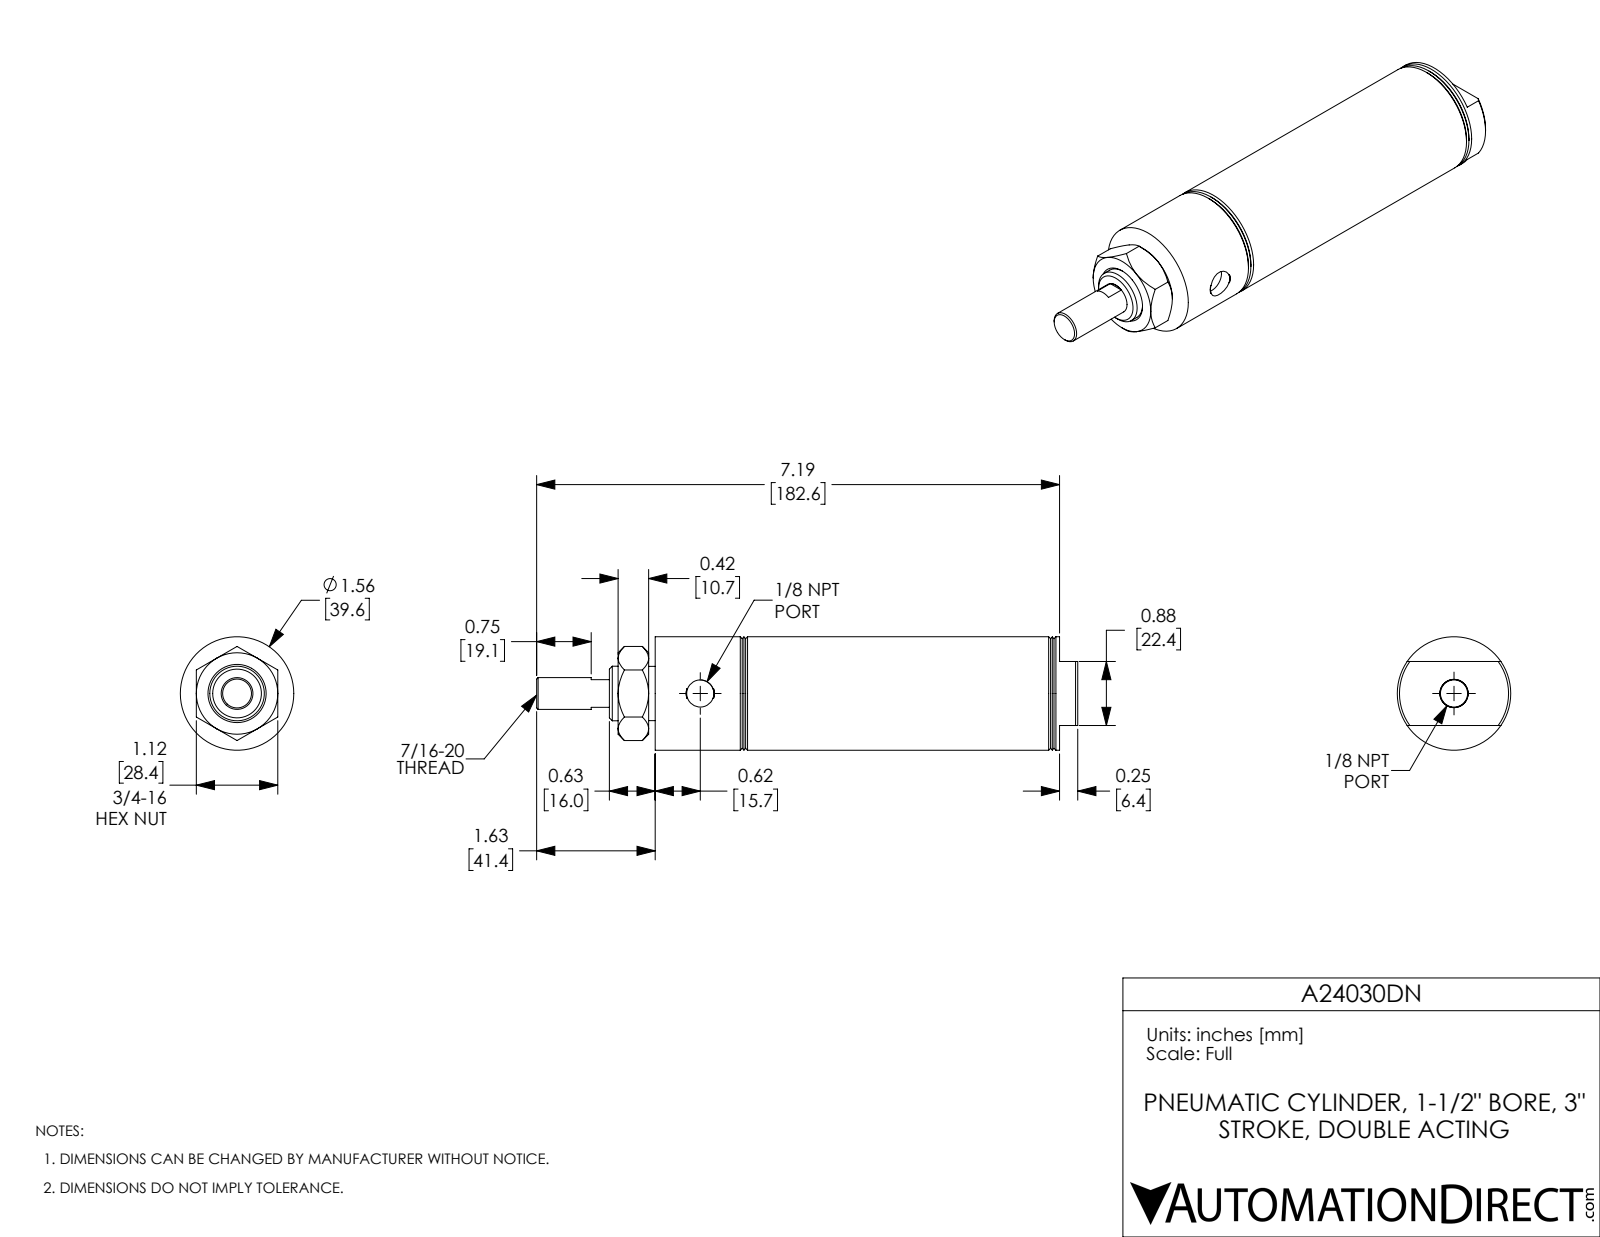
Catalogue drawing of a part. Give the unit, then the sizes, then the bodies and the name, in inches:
Units: inches
Overall size (bounding box): 7.44 × 1.56 × 1.56
Round holes (diameter × count): ⌀0.374 ×2, ⌀0.437 ×1, ⌀0.75 ×1, ⌀1.5 ×1
Round bosses / shafts (diameter × count): ⌀1.56 ×1, ⌀0.746 ×1
Main face-to-face distances: 0.5, 3.5, 3, 4.84, 4.34, 1.34, 0.97, 1.47, 4.47, 5.81
Volume: 6.731 in³ · Surface area: 74.59 in²
Bodies: 3 solids, 104 faces (32 planar, 24 cylindrical, 48 other)
Part name (STEP PRODUCT): A24030DN; A24030DN_Mounting Nut_D-3556; A24030DN-Rod; A24030DN-MainBody
STEP written by: SolidWorks 2017 (AUTOMOTIVE_DESIGN)
